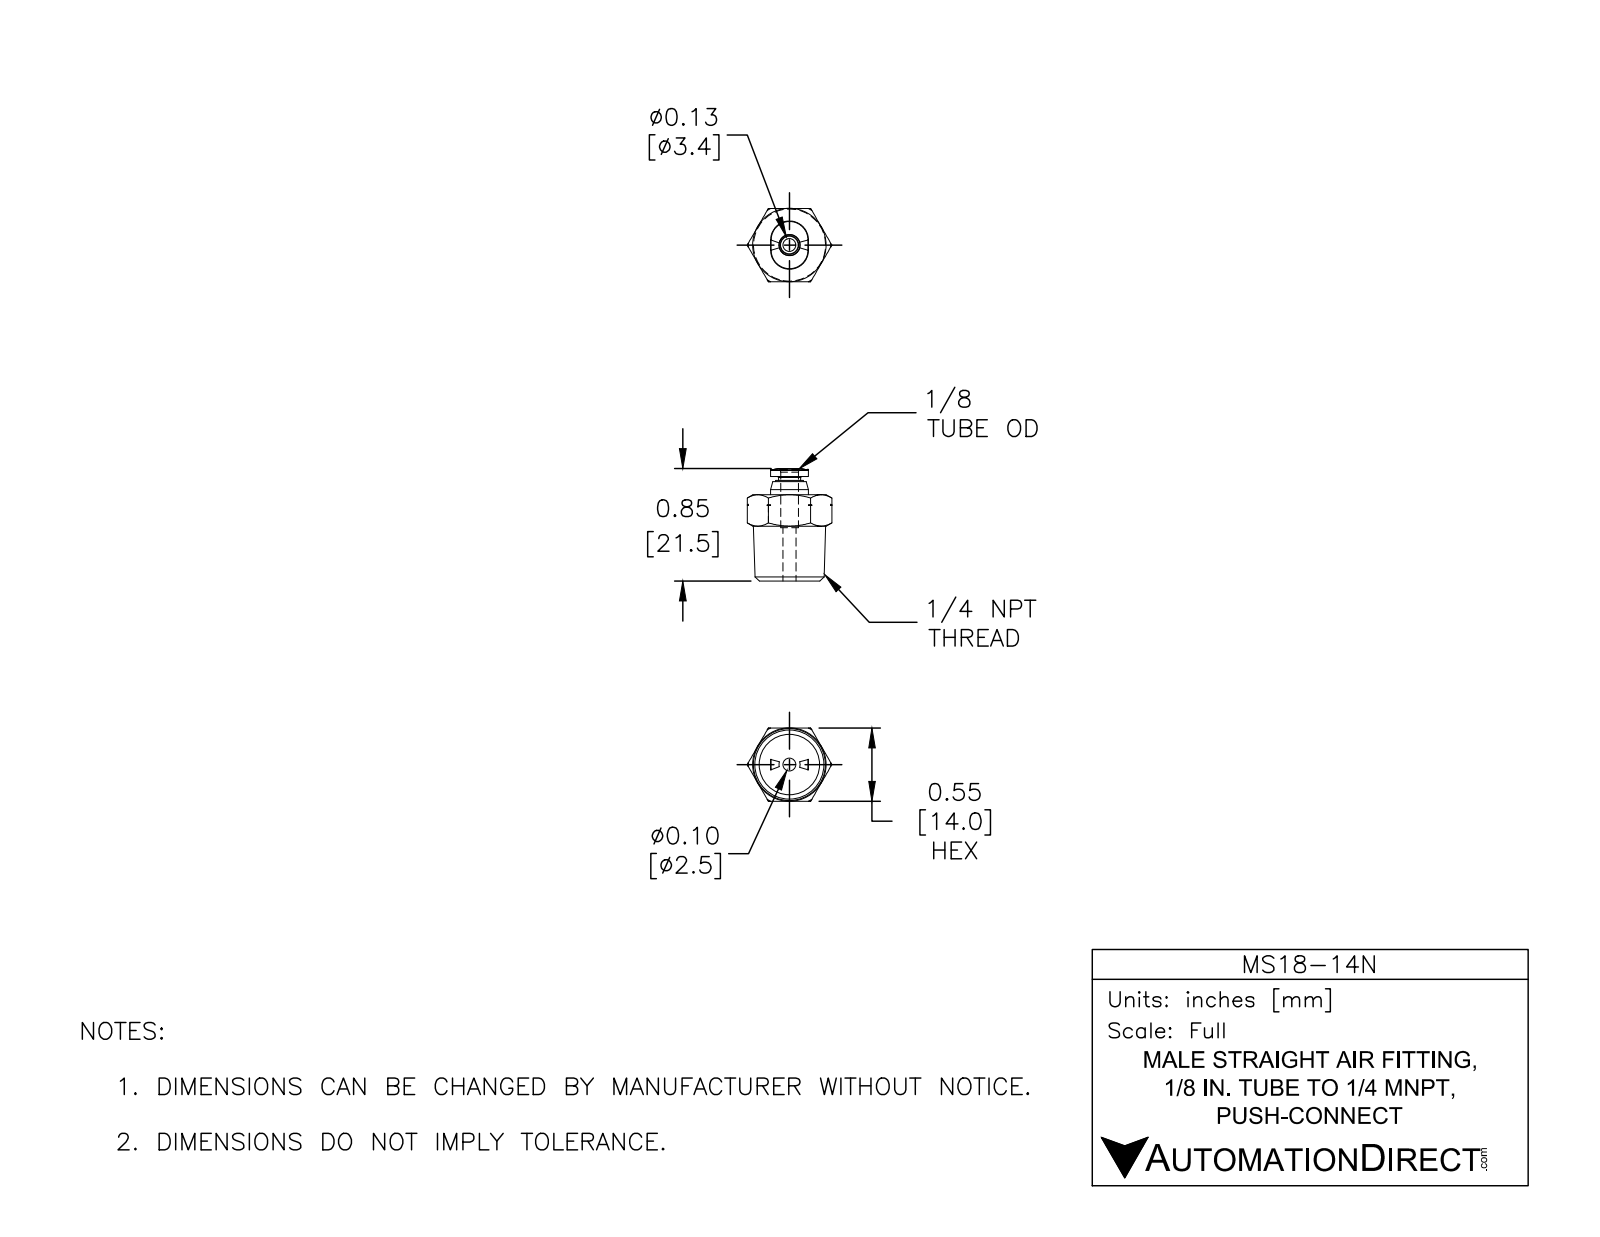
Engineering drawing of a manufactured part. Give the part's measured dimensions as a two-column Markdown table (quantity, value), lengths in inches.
| quantity | value |
| --- | --- |
| part name | MS18-14N |
| STEP written by | SolidWorks 2015 (CONFIG_CONTROL_DESIGN) |
| units | inches |
| bodies | 1 solid, 80 faces (16 planar, 12 cylindrical, 52 other) |
| overall size | 0.846 × 0.636 × 0.551 |
| volume | 0.154 in³ |
| surface area | 2.155 in² |
| round holes (diameter × count) | 0.098 × 1, 0.134 × 1 |
| round bosses / shafts (diameter × count) | 0.283 × 1, 0.209 × 1, 0.165 × 1 |
| partial cylindrical surfaces (radius × count) | 0.142 × 2 |
| main face-to-face distances | 0.551, 0.65, 0.787, 0.138, 0.098, 0.748, 0.039, 0.758, 0.108, 0.03 |
